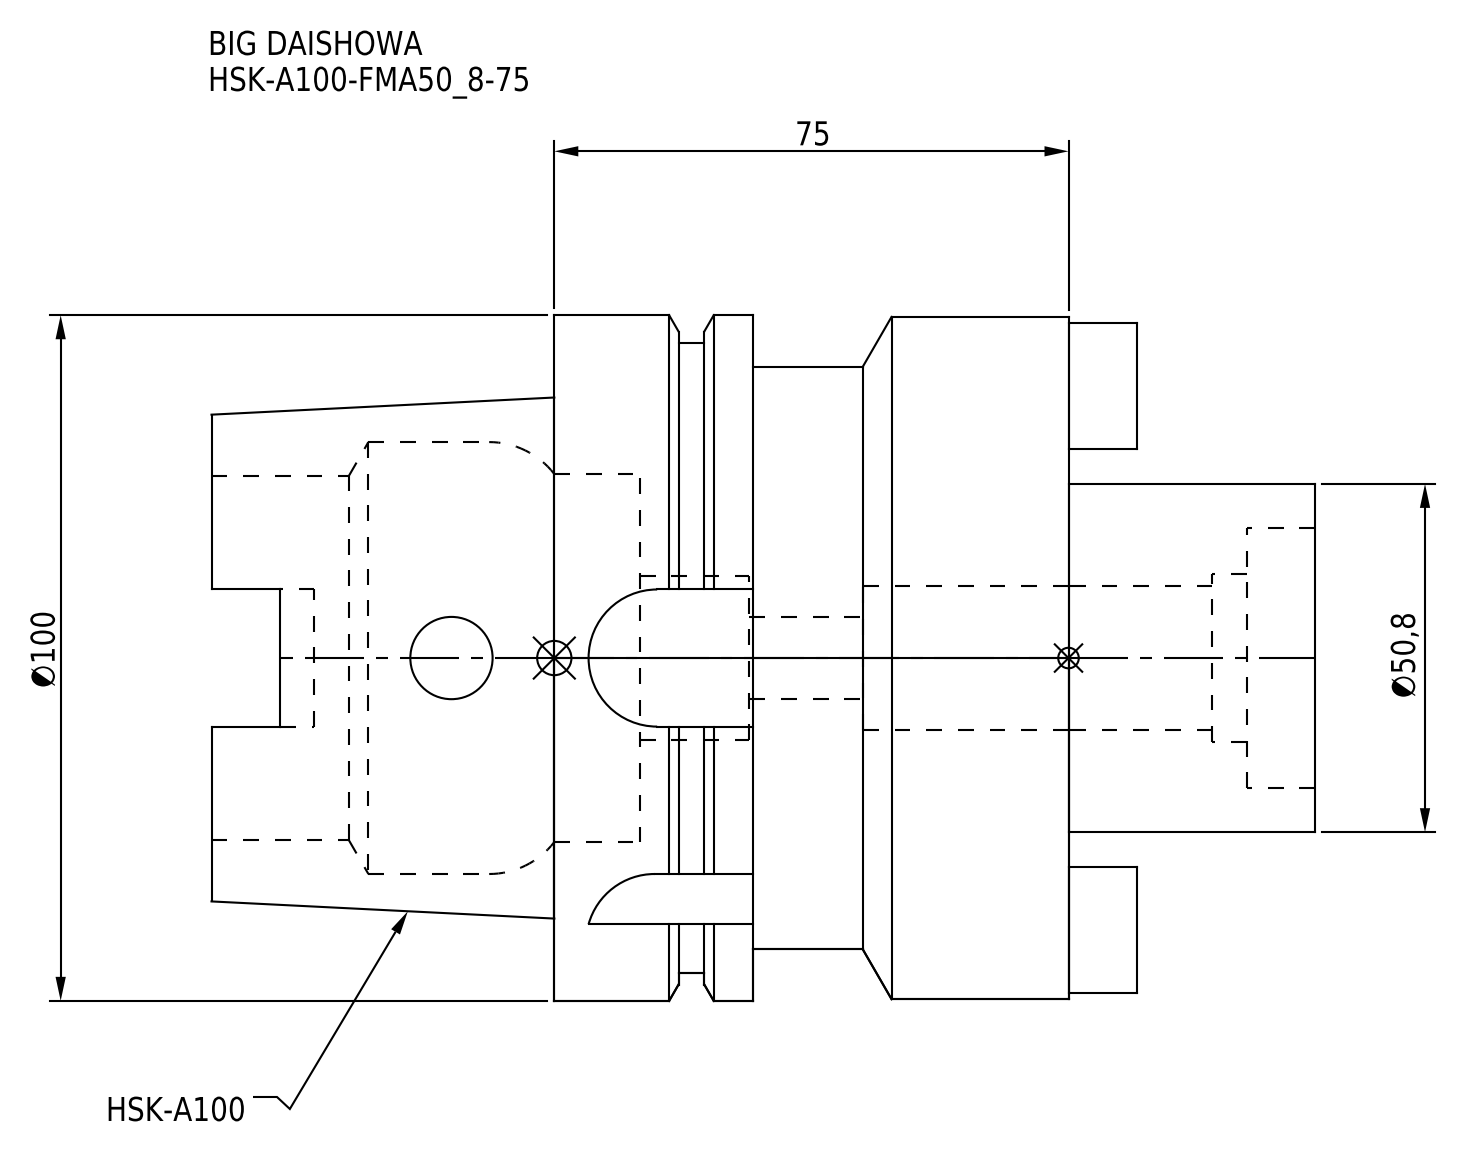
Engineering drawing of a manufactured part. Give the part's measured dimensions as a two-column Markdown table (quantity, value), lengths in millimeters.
| quantity | value |
| --- | --- |
| part name | HSK-A100-FMA50_8-75 |
| STEP written by | CREO PARAMETRIC BY PTC INC, 2016380 (AUTOMOTIVE_DESIGN) |
| units | millimeters |
| bodies | 1 solid, 108 faces (46 planar, 46 cylindrical, 16 other) |
| overall size | 161 × 100 × 100 |
| volume | 619 754 mm³ |
| surface area | 79 444 mm² |
| round holes (diameter × count) | 12 × 2, 21 × 1, 24 × 1, 24.5 × 1, 38 × 1, 53 × 1, 53.8 × 1, 63 × 1 |
| round bosses / shafts (diameter × count) | 100 × 1, 99.5 × 1, 92 × 1, 85 × 1, 50.8 × 1 |
| partial cylindrical surfaces (radius × count) | 4.88 × 4, 10 × 4 |
| main face-to-face distances | 75, 16.55, 46, 29, 62.55, 12.45, 10, 26, 125, 16 |
